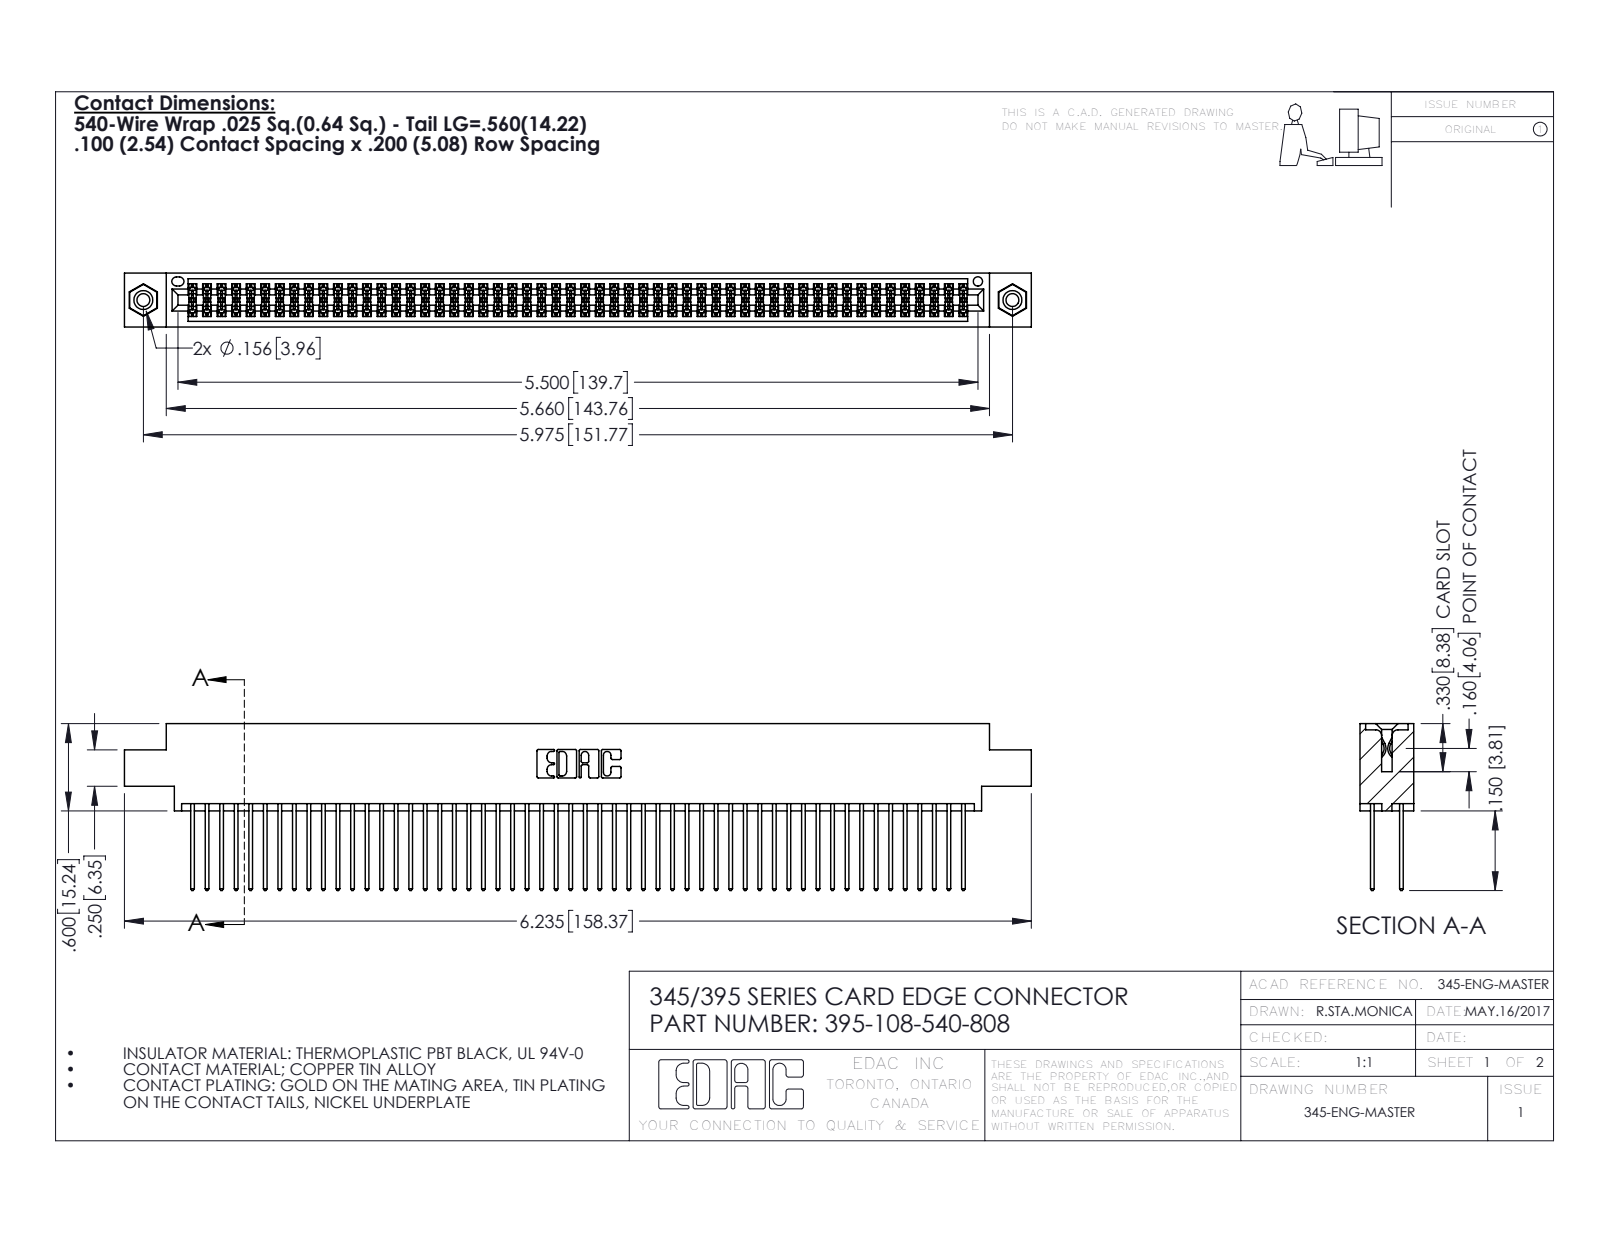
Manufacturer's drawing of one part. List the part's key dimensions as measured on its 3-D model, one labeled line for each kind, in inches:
Part name (STEP PRODUCT): 395-108-540-808; 345-292-001_345-293-140; 345 Part_0.170 Offset - 0.156 Dia-TI; 345-250-001_345-250-003-102
STEP written by: SolidWorks 2016 (CONFIG_CONTROL_DESIGN)
Units: inches
Bodies: 111 solids, 5590 faces (3680 planar, 1894 cylindrical, 16 other)
Overall size (bounding box): 6.235 × 1.147 × 0.37
Volume: 0.963 in³ · Surface area: 39.71 in²
Round holes (diameter × count): ⌀0.089 ×2, ⌀0.125 ×2, ⌀0.156 ×2, ⌀0.064 ×1
Round bosses / shafts (diameter × count): ⌀0.155 ×2
Partial cylindrical surfaces — rounded edges, fillets, slot ends (radius × count): R0.006 ×162, R0.01 ×108, R0.01 ×22, R0.007 ×6, R0.031 ×6, R0.026 ×3, R0.014 ×2, R0.019 ×2
Main face-to-face distances: 0.072, 0.298, 0.2, 0.098, 0.272, 0.025, 0.37, 0.225, 0.175, 0.149
Hole centre spacings: 0.27, 5.739, 5.975
